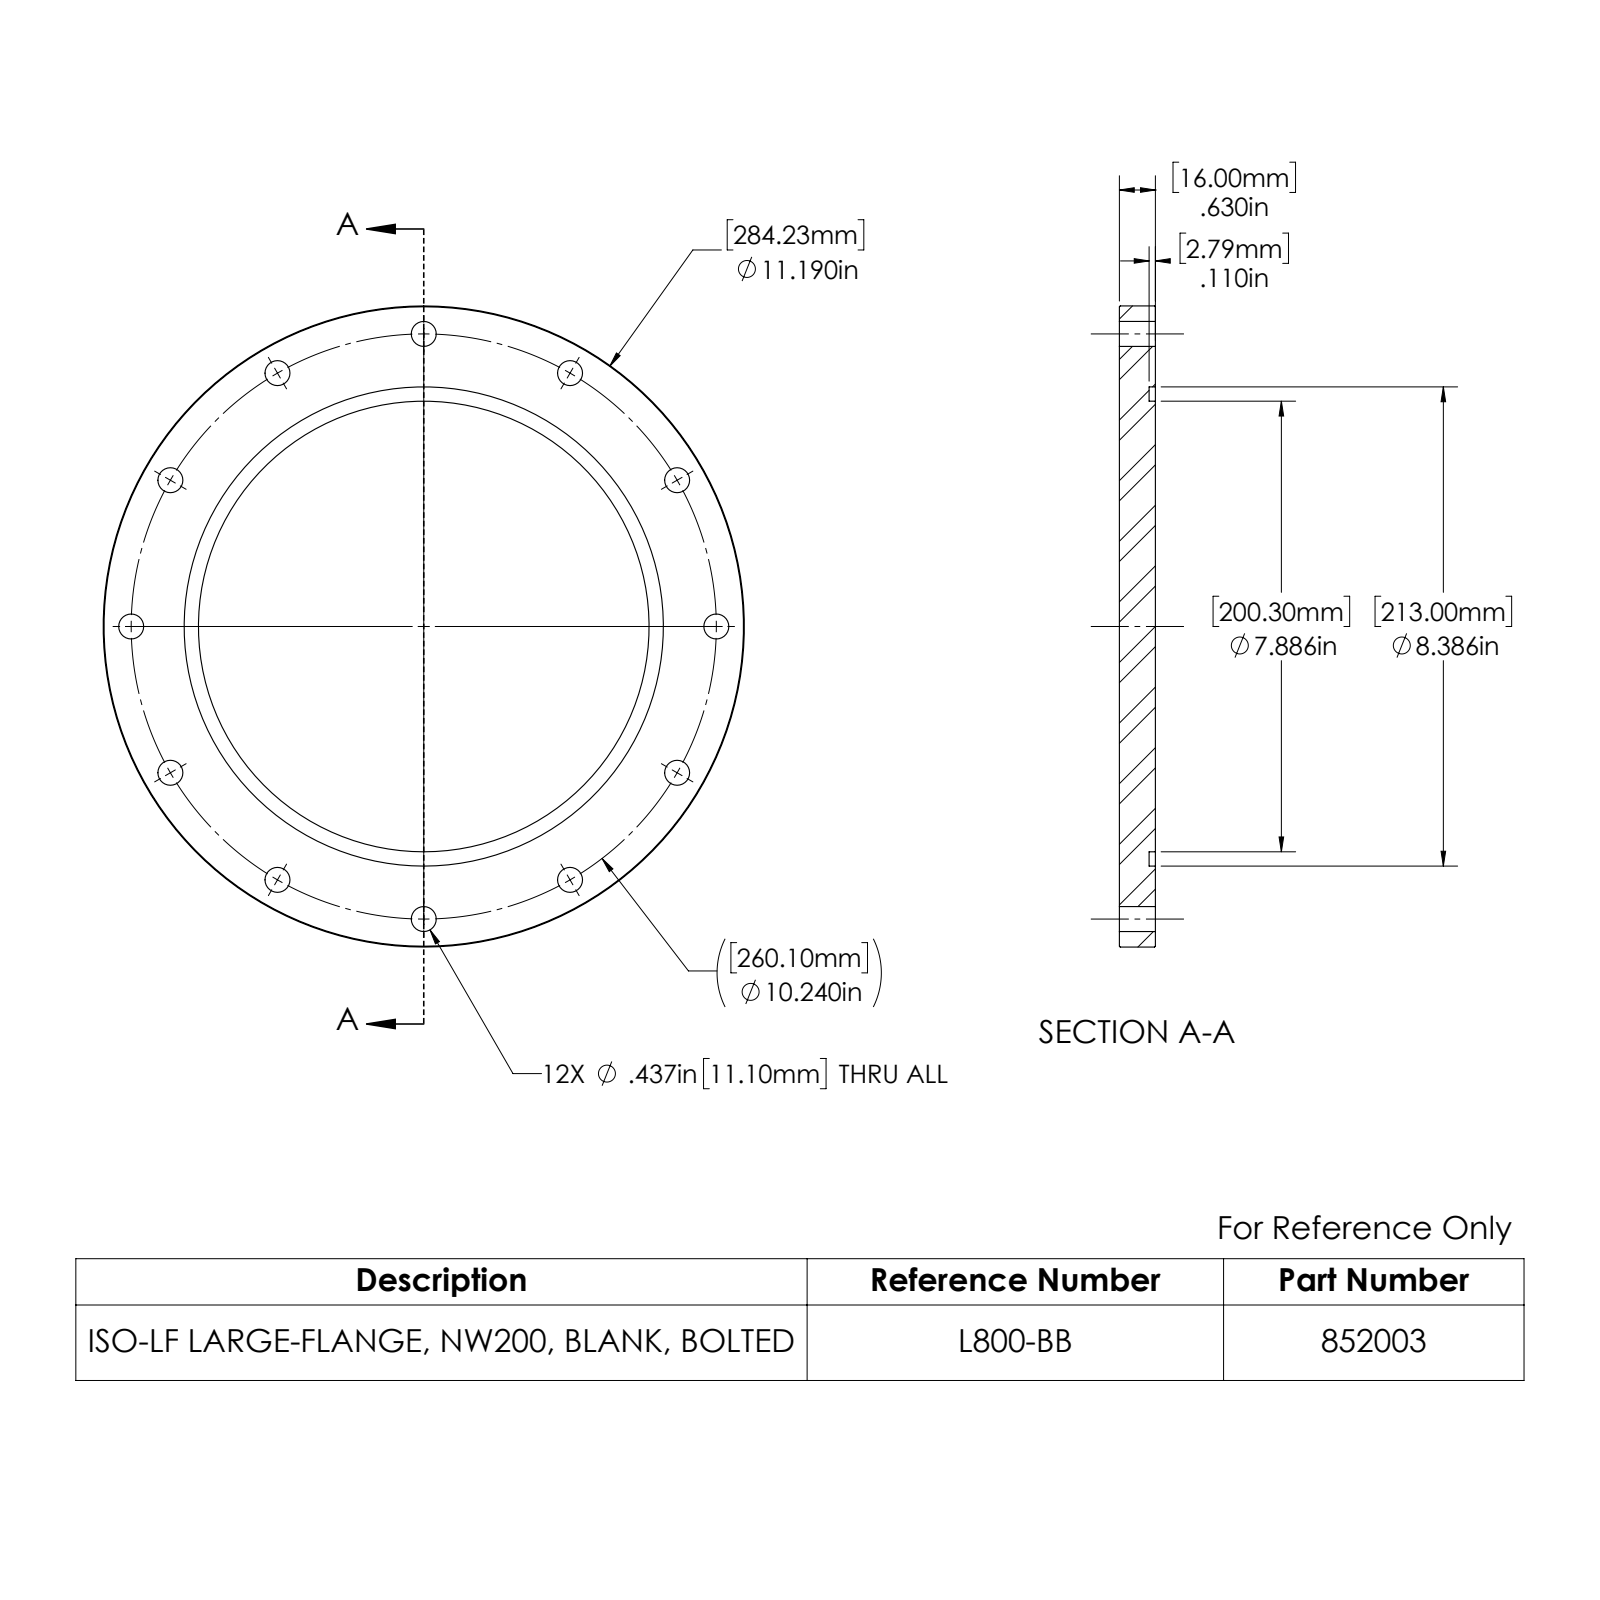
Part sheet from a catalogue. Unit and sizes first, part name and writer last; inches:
Units: inches
Overall size (bounding box): 11.22 × 11.22 × 0.63
Round holes (diameter × count): ⌀0.437 ×12, ⌀8.386 ×1
Round bosses / shafts (diameter × count): ⌀11.22 ×1, ⌀7.886 ×1
Main face-to-face distances: 0.63, 0.11, 0.52
Hole centre spacings: 2.65, 5.12, 5.12, 7.241, 8.868, 9.891, 7.241, 8.868
Volume: 60.44 in³ · Surface area: 231.7 in²
Bodies: 1 solid, 38 faces (4 planar, 30 cylindrical, 4 other)
Part name (STEP PRODUCT): 852003
STEP written by: SolidWorks 2022 (AUTOMOTIVE_DESIGN)
